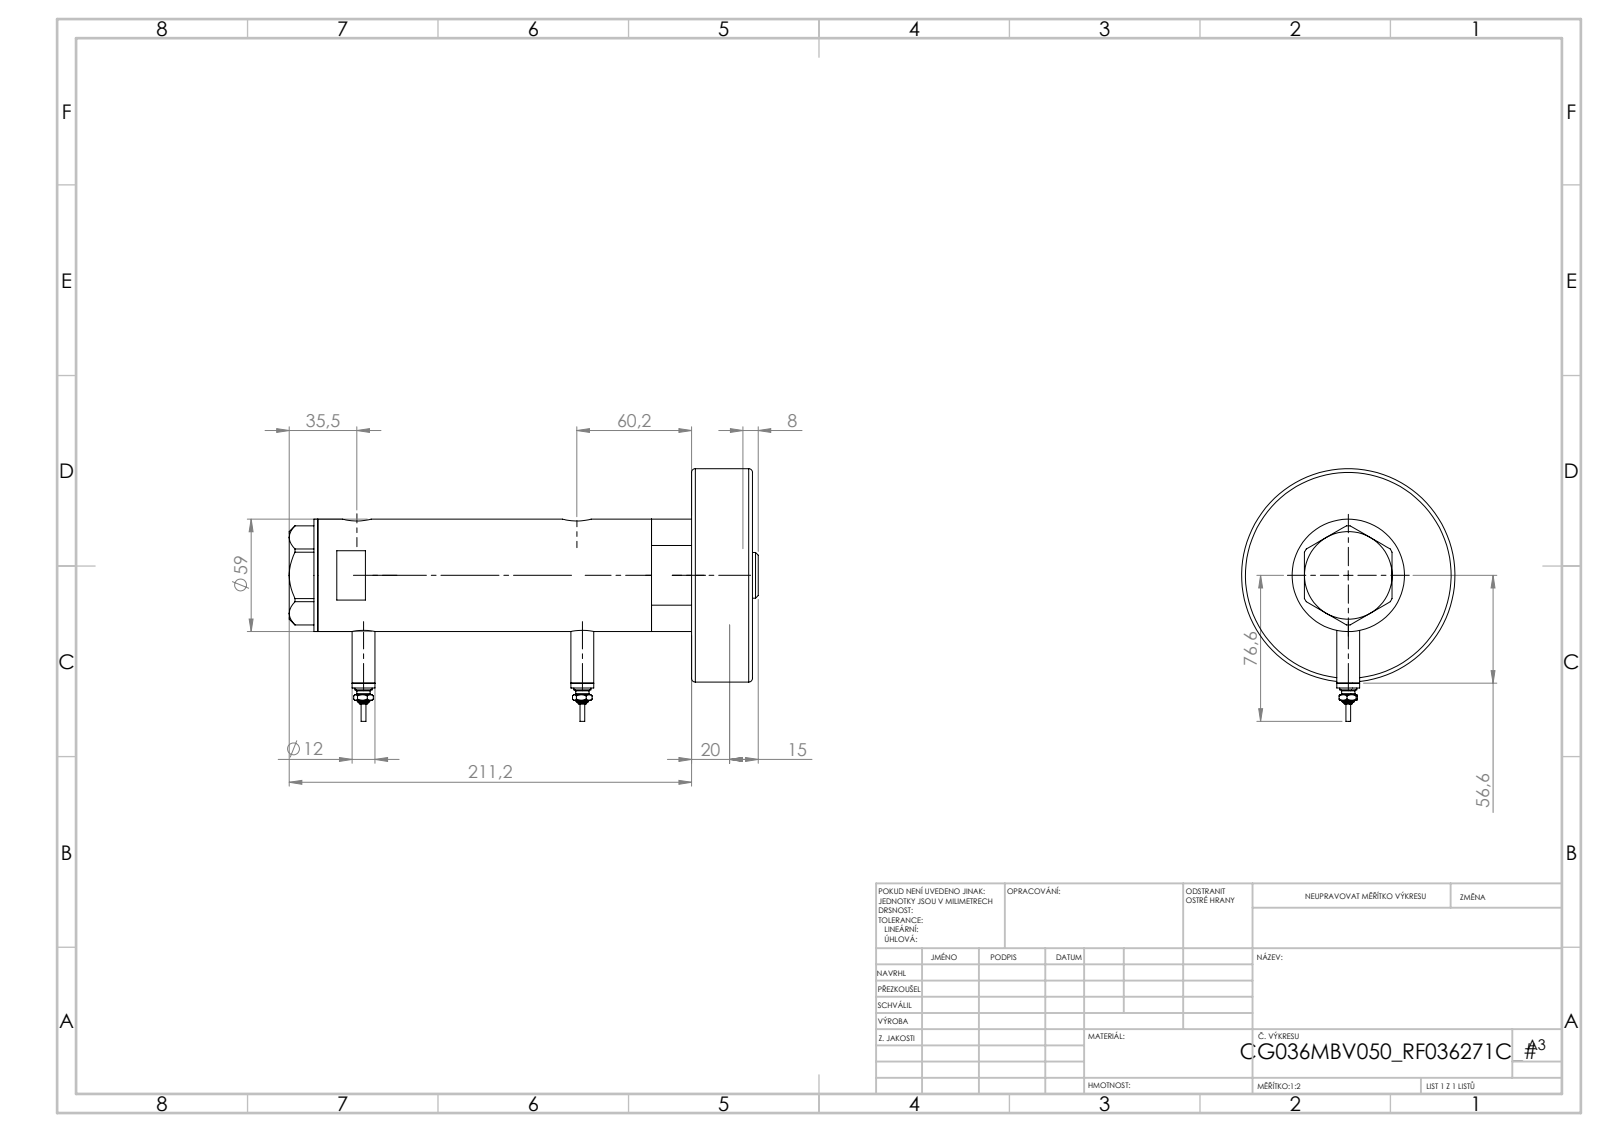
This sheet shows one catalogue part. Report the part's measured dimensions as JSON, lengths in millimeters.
{"part_name": "V270CG_VC; Switch; V270CG_271C; V270CG_FRONT (+2 more)", "step_written_by": "SolidWorks 2019 (CONFIG_CONTROL_DESIGN)", "units": "millimeters", "bodies": {"solids": 7, "faces": 222, "planar": 81, "cylindrical": 73, "other": 68}, "overall_size": [246.2, 132.6, 112], "volume_mm3": 836907, "surface_area_mm2": 148720, "round_holes": [[9.73, 2], [12.5, 2], [15, 2], [8.5, 1], [25, 1], [26.5, 1], [36, 1], [40, 1], [48, 1], [52, 1]], "round_bosses_or_shafts": [[12, 2], [9, 2], [7, 2], [4.5, 2], [2.5, 2], [112, 1], [59, 1], [46, 1]], "face_to_face_distances": [32, 196.2, 228.2, 137.2, 59, 91, 23.5, 113.7, 172.7, 204.7], "hole_center_spacings": [2.9, 3.5, 112, 114.9, 115.5, 118.4]}
